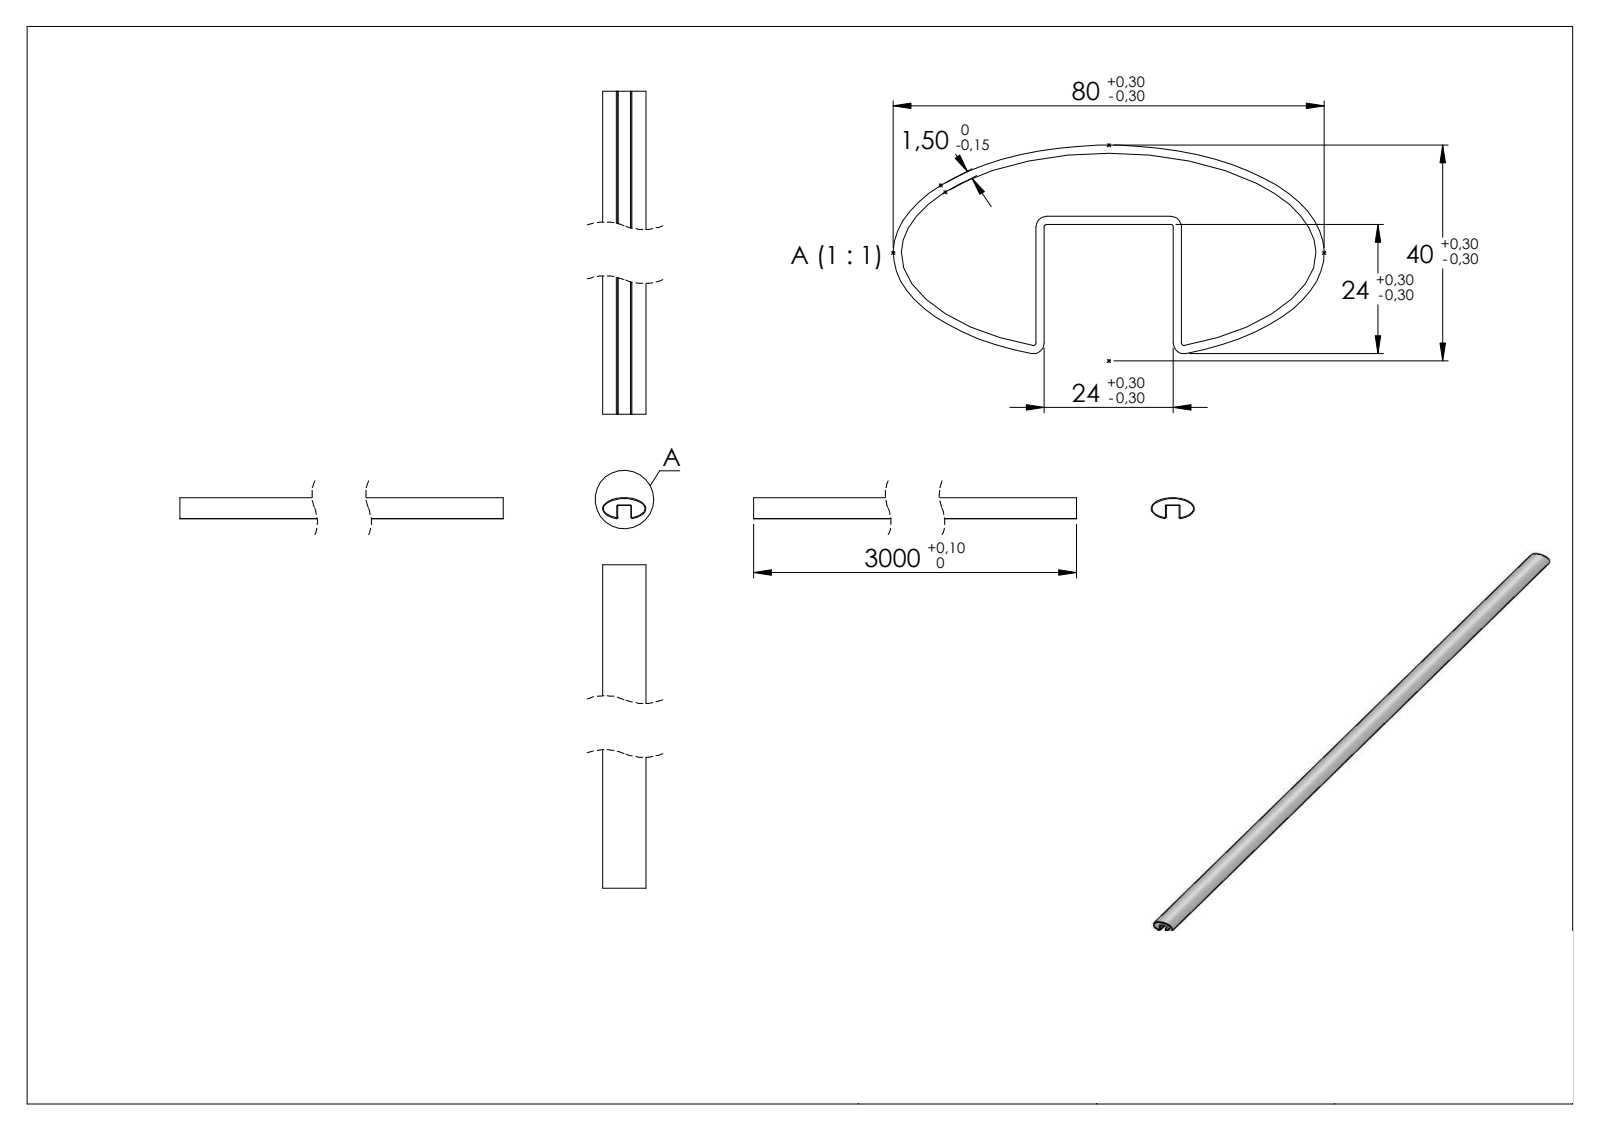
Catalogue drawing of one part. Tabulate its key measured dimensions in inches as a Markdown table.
| quantity | value |
| --- | --- |
| part name | 60332-2403M |
| STEP written by | SolidWorks 2018 (CONFIG_CONTROL_DESIGN) |
| units | inches |
| bodies | 1 solid, 324 faces (165 planar, 8 cylindrical, 151 other) |
| overall size | 118.11 × 3.15 × 1.524 |
| volume | 66.88 in³ |
| surface area | 2 186 in² |
| partial cylindrical surfaces (radius × count) | 0.02 × 4, 0.079 × 4 |
| main face-to-face distances | 0.059, 1.004, 1.063, 0.945, 118.11, 0.055, 0.129, 0.106, 0.013, 0.531 |
